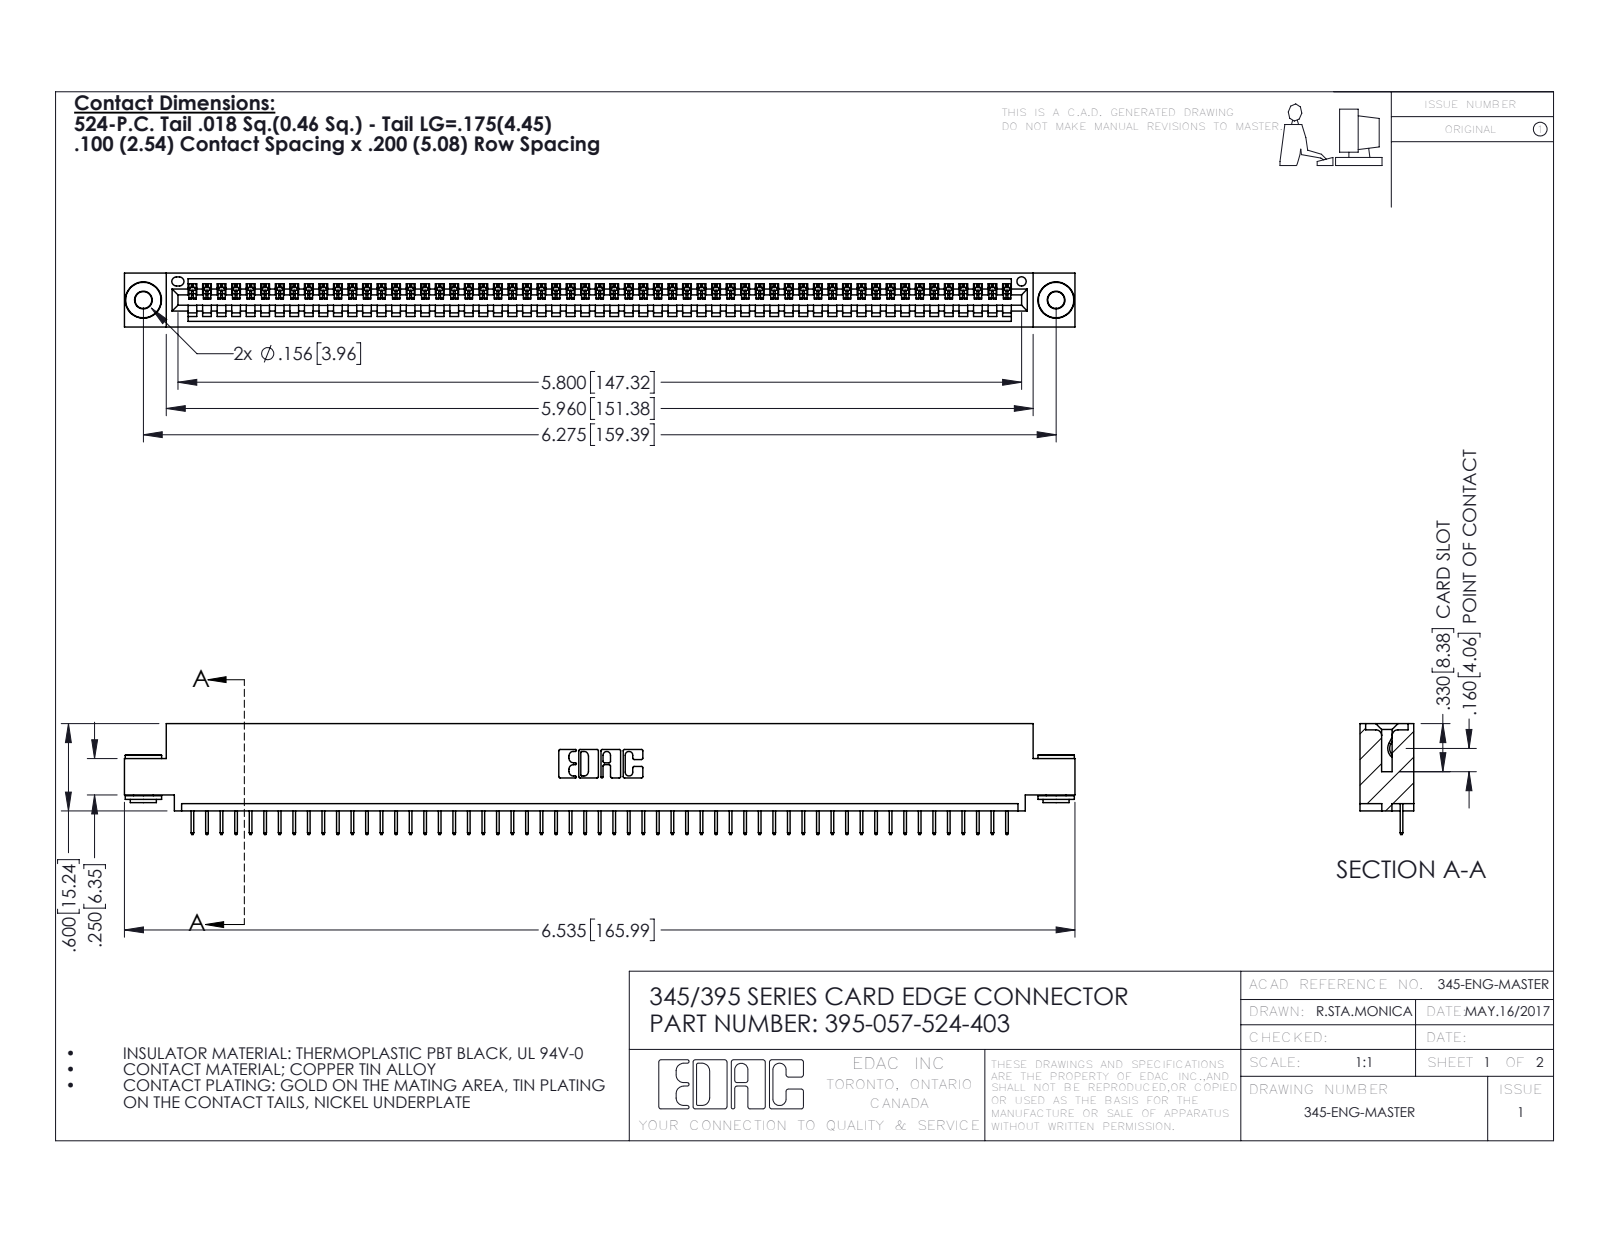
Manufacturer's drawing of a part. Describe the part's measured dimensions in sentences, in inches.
The part is named "345-250-002_345-250-002-102; 345-292-001_345-293-124; 345 Part_0.110 Offset - 0.156 Dia-TH; 395-057-524-403". Its 3-D file was written by "SolidWorks 2016 (CONFIG_CONTROL_DESIGN)". It is 60 solids with 3702 faces: 2716 planar, 978 cylindrical and 8 other. Overall it measures 6.535 by 0.762 by 0.37 inches. Its volume is 0.953 cubic inches and its surface area 31.81 square inches. Round holes: 2 of diameter 0.116, 2 of diameter 0.156, 1 of diameter 0.064. Round bosses or shafts: 2 of diameter 0.25, 2 of diameter 0.18, 2 of diameter 0.136. Partial cylindrical surfaces (rounded edges, fillets, slot ends): 114 of radius 0.006, 22 of radius 0.01, 6 of radius 0.007, 6 of radius 0.031, 3 of radius 0.026, 2 of radius 0.031, 2 of radius 0.04, 1 of radius 0.014. The main face-to-face distances are 0.072, 0.298, 0.37, 0.2, 0.025, 0.098, 0.272, 0.225, 0.072, 0.149. The hole center spacings are 0.27, 6.039, 6.275.
